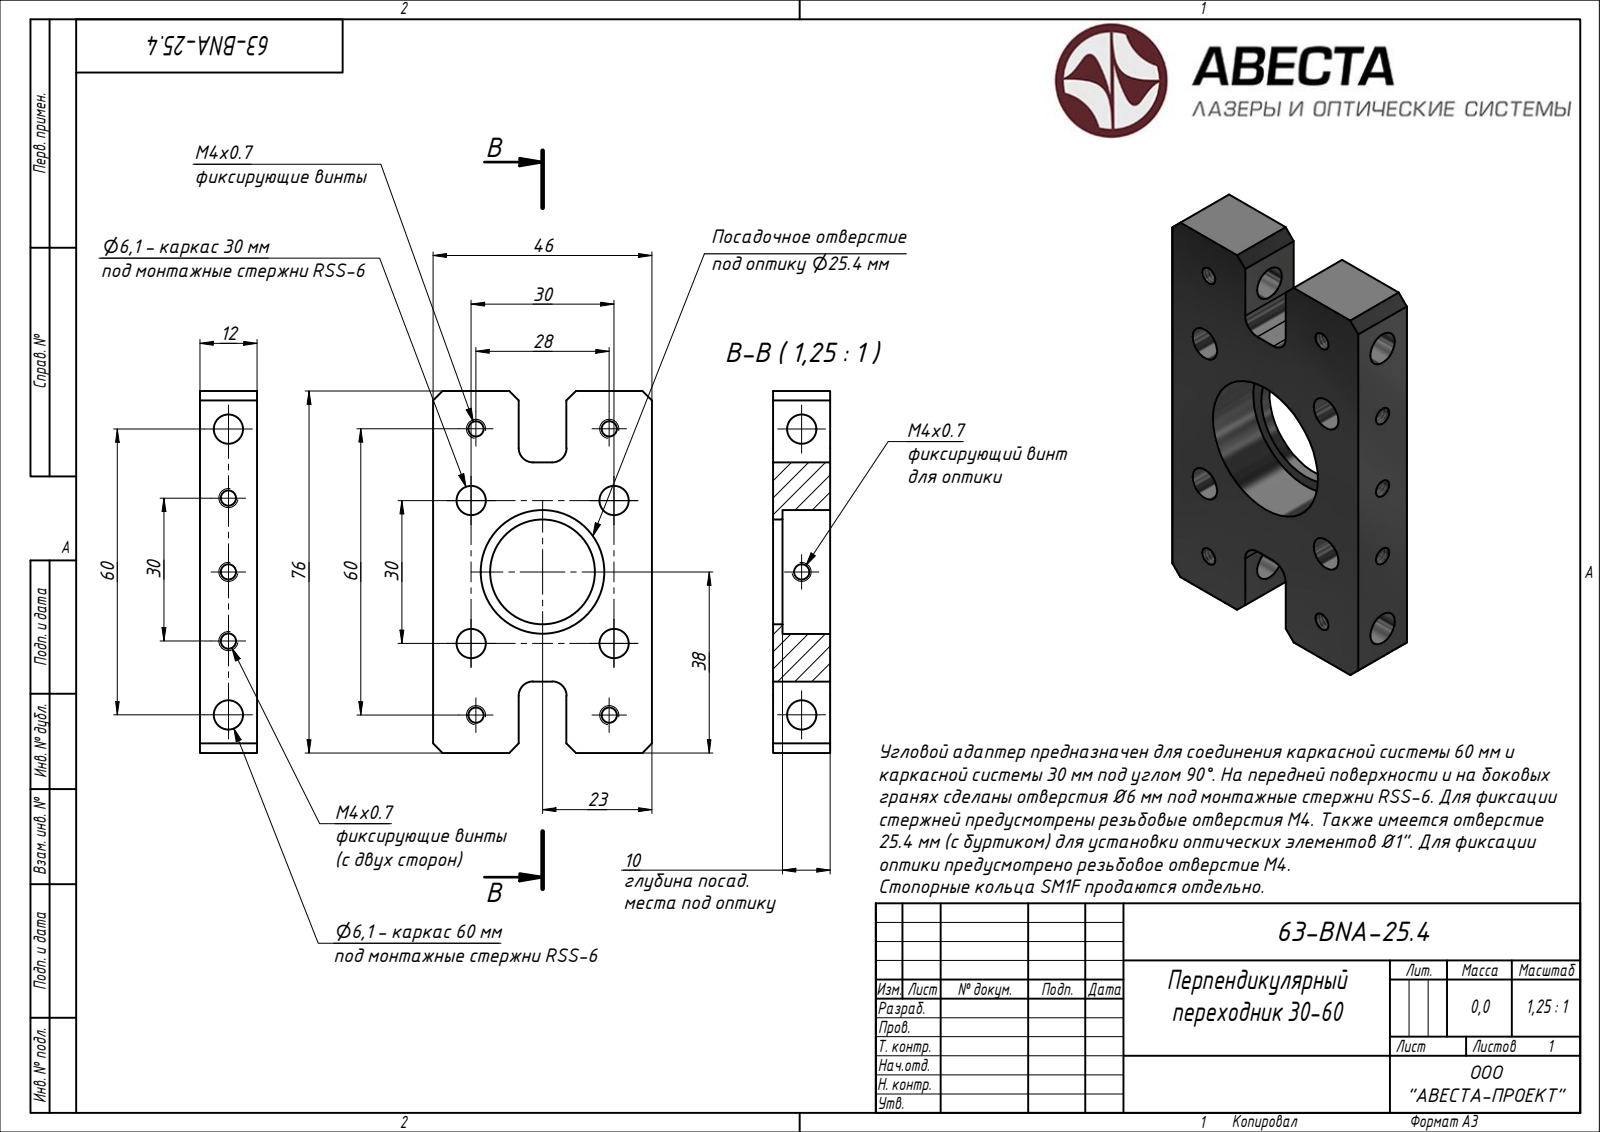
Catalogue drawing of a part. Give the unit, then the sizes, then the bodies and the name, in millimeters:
Units: millimetres
Overall size (bounding box): 76 × 46 × 12
Round holes (diameter × count): ⌀3.24 ×7, ⌀6.1 ×6, ⌀22 ×1, ⌀26 ×1
Partial cylindrical surfaces — rounded edges, fillets, slot ends (radius × count): R3 ×4
Main face-to-face distances: 12, 46, 18, 28, 76, 10, 2, 19.79, 63.63, 15
Hole centre spacings: 30, 15.08, 21.21, 32.67, 33.15, 45.06, 53.58, 14.5
Volume: 28 324 mm³ · Surface area: 12 169 mm²
Bodies: 1 solid, 46 faces (23 planar, 23 cylindrical, 0 other)
Part name (STEP PRODUCT): 63-BNA-25.4
STEP written by: Autodesk Inventor 2020 (AUTOMOTIVE_DESIGN)
